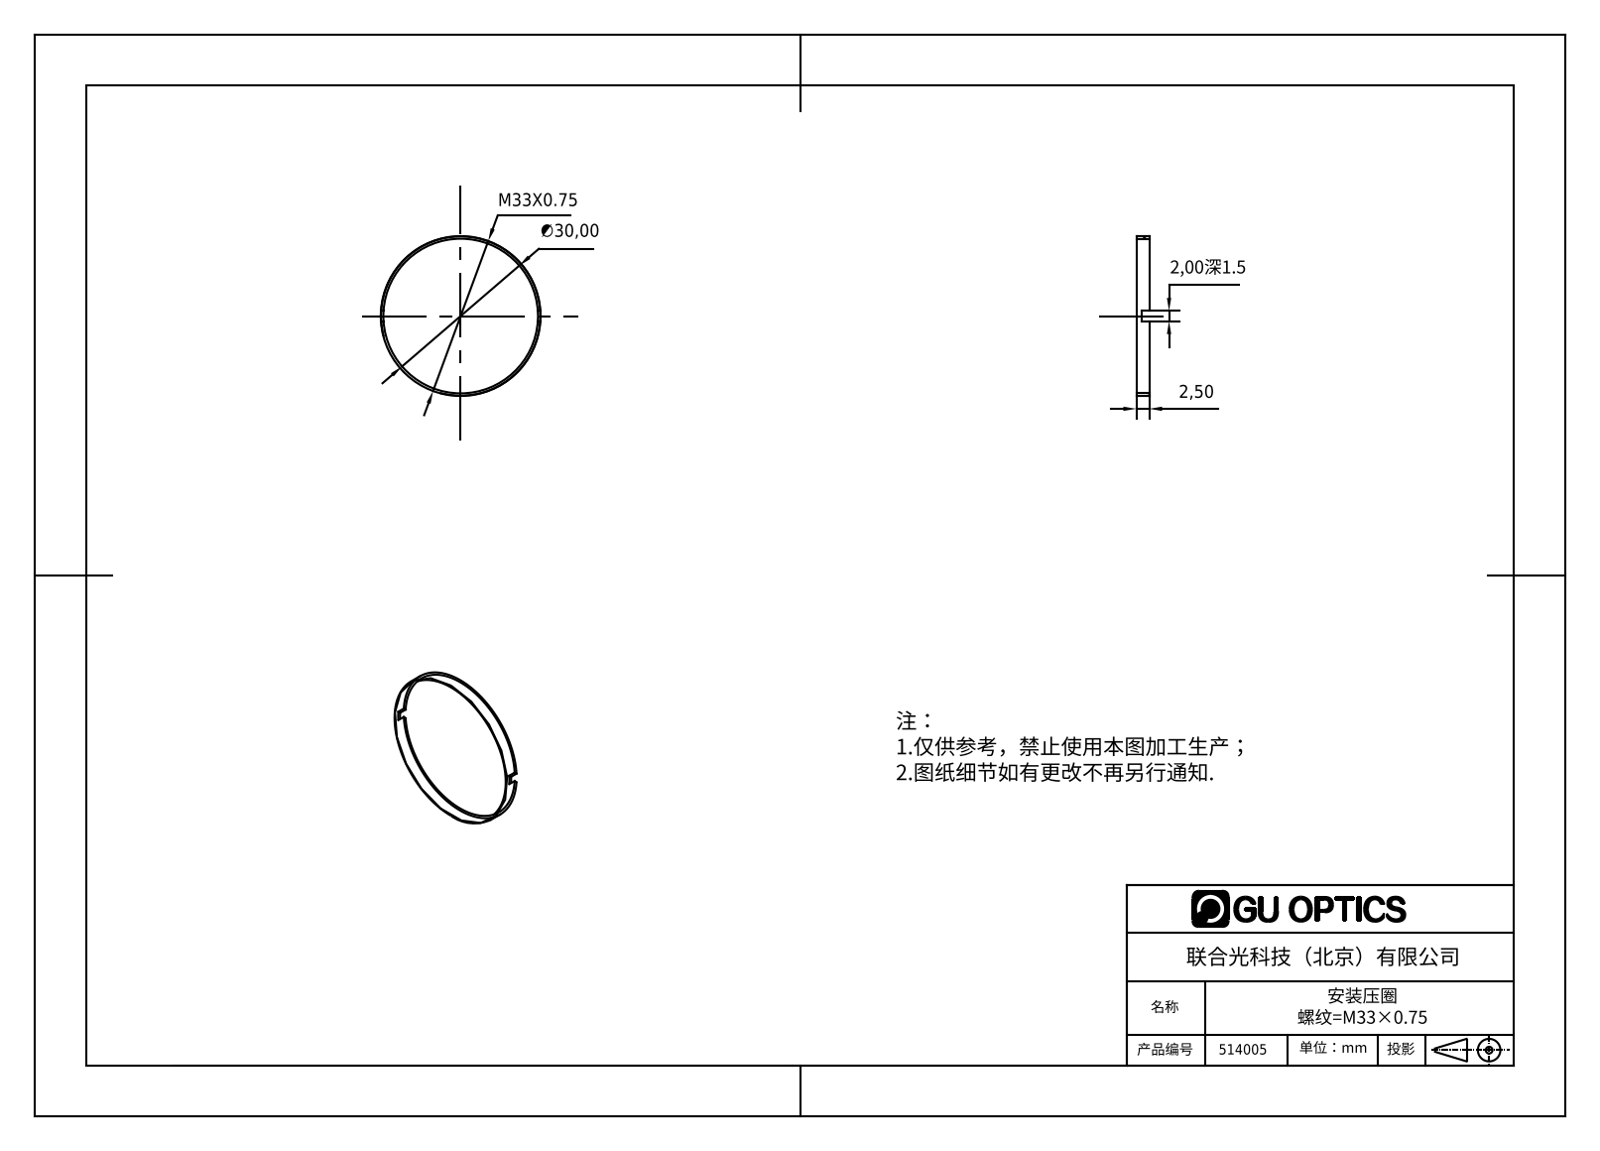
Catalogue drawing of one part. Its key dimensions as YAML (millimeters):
part_name: "514006"
step_written_by: "SolidWorks 2016 (AUTOMOTIVE_DESIGN)"
units: millimeters
bodies: {solids: 1, faces: 13, planar: 9, cylindrical: 4, other: 0}
overall_size: [32, 32, 2.5]
volume: 237
surface_area: 676
round_holes:
  - {diameter: 30, count: 1}
round_bosses_or_shafts:
  - {diameter: 32, count: 1}
face_to_face_distances: [2.5, 1, 1.5, 2]
